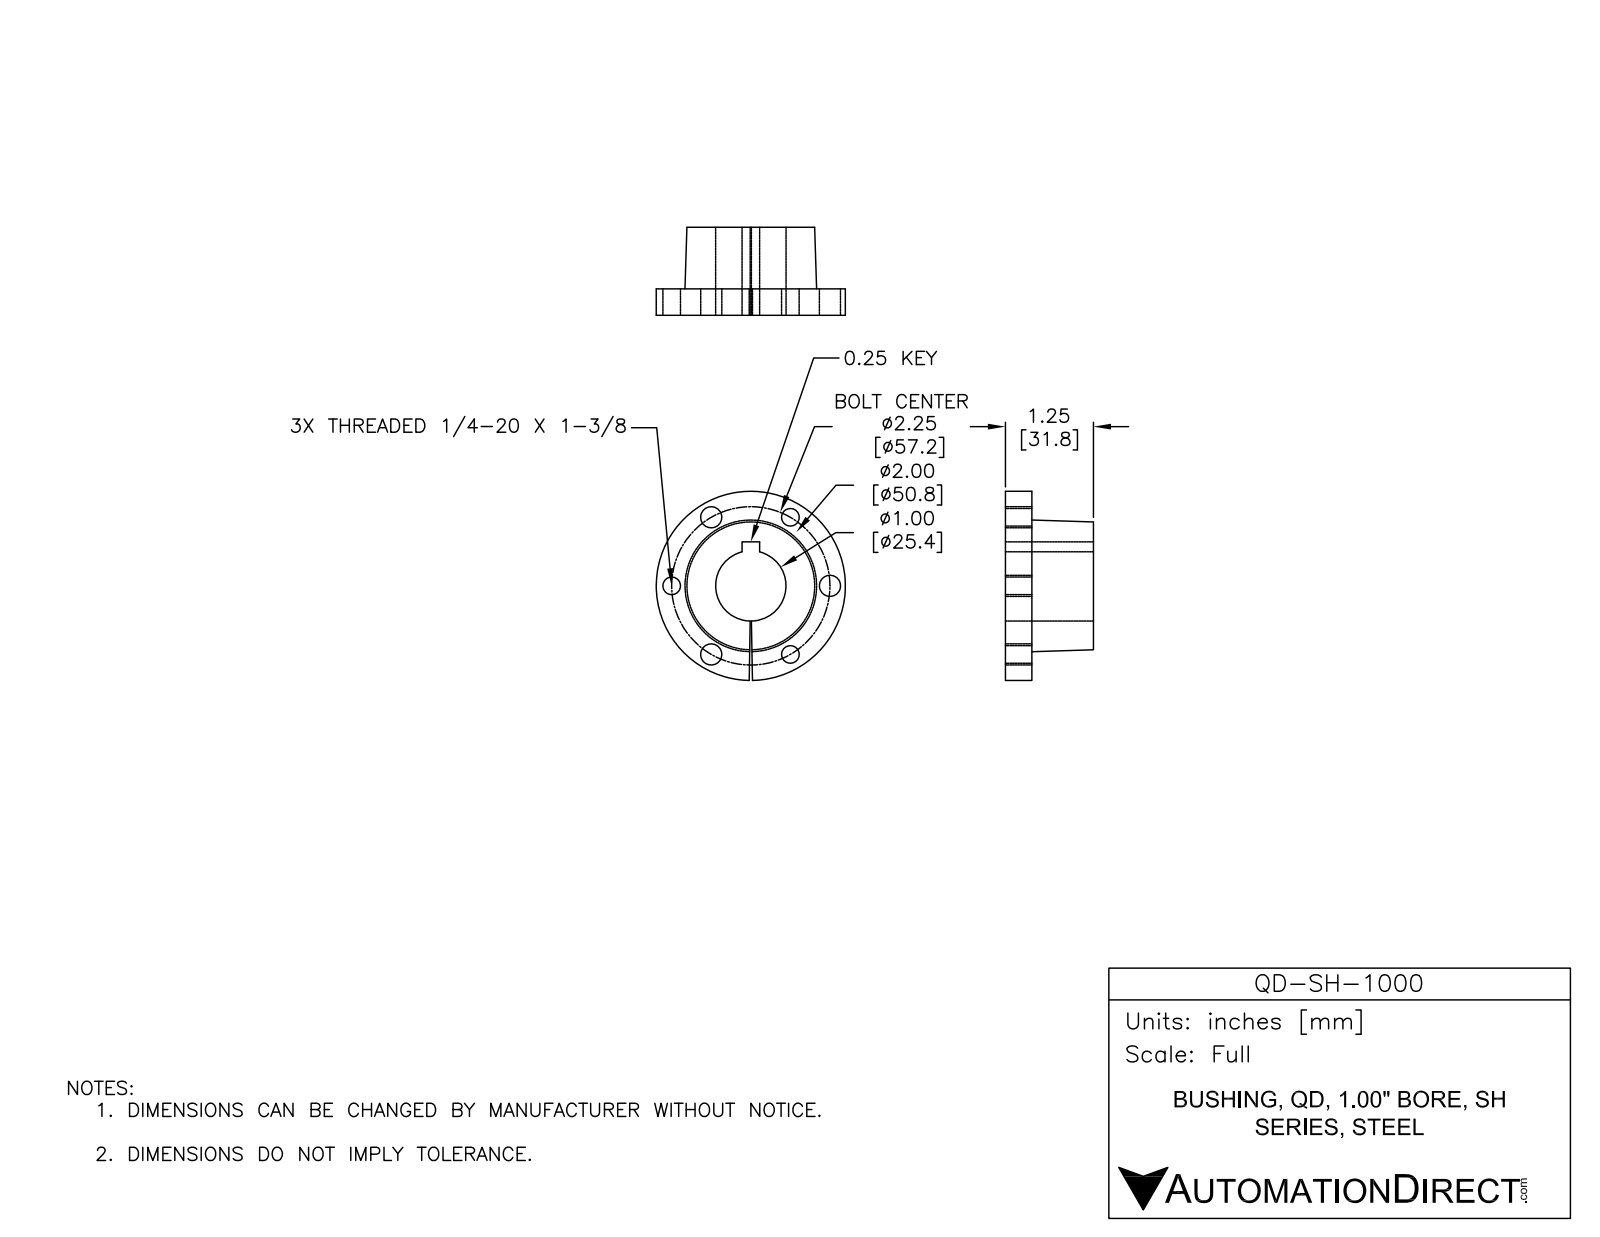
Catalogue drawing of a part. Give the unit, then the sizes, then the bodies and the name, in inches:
Units: inches
Overall size (bounding box): 2.688 × 2.687 × 1.25
Round holes (diameter × count): ⌀0.25 ×3, ⌀0.3 ×3, ⌀1 ×1
Round bosses / shafts (diameter × count): ⌀2.687 ×1
Main face-to-face distances: 0.375, 1.25, 0.875, 0.25
Hole centre spacings: 1.125, 1.125, 1.948, 1.949, 2.25, 2.25
Volume: 3.287 in³ · Surface area: 24.54 in²
Bodies: 1 solid, 29 faces (8 planar, 18 cylindrical, 3 other)
Part name (STEP PRODUCT): QD-SH-1000
STEP written by: SolidWorks 2014 (AUTOMOTIVE_DESIGN)
